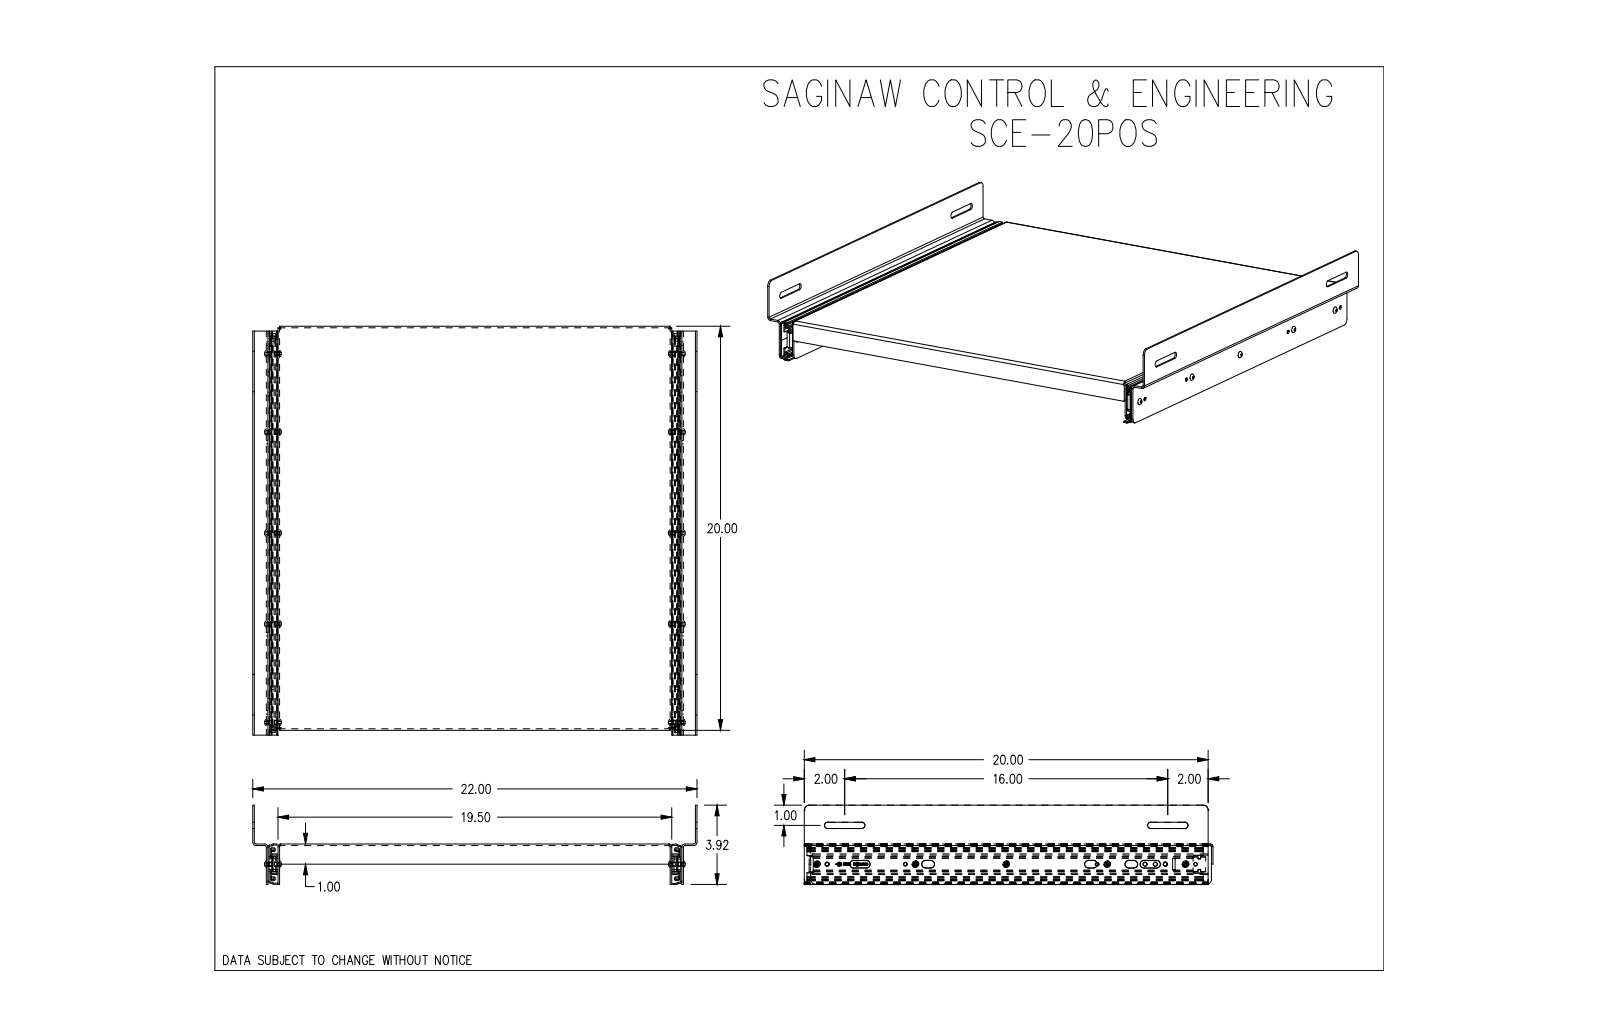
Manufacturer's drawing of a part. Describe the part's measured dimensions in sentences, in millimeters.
The part is named "SCE-20POS". Its 3-D file was written by "SolidWorks 2019 (CONFIG_CONTROL_DESIGN)". It is 29 solids with 710 faces: 332 planar, 290 cylindrical and 88 other. Overall it measures 558.8 by 514.1 by 99.8 millimeters. Its volume is 1 112 000 cubic millimeters and its surface area 1 234 000 square millimeters. Round holes: 25 of diameter 5.1, 14 of diameter 4.4, 10 of diameter 2.5, 10 of diameter 4. Round bosses or shafts: 10 of diameter 5.5, 10 of diameter 4.1. Partial cylindrical surfaces (rounded edges, fillets, slot ends): 20 of radius 0.8, 16 of radius 1.6, 10 of radius 4.8, 6 of radius 1.5, 6 of radius 6.4, 4 of radius 0.5, 4 of radius 0.9, 4 of radius 1. The main face-to-face distances are 2, 508, 14.7, 31.8, 17.1, 525.1, 539.8, 12.7, 506, 1.4. The hole center spacings are 12.7, 425.5, 12.8, 12.6, 25.4, 38, 38.1, 111.1.
